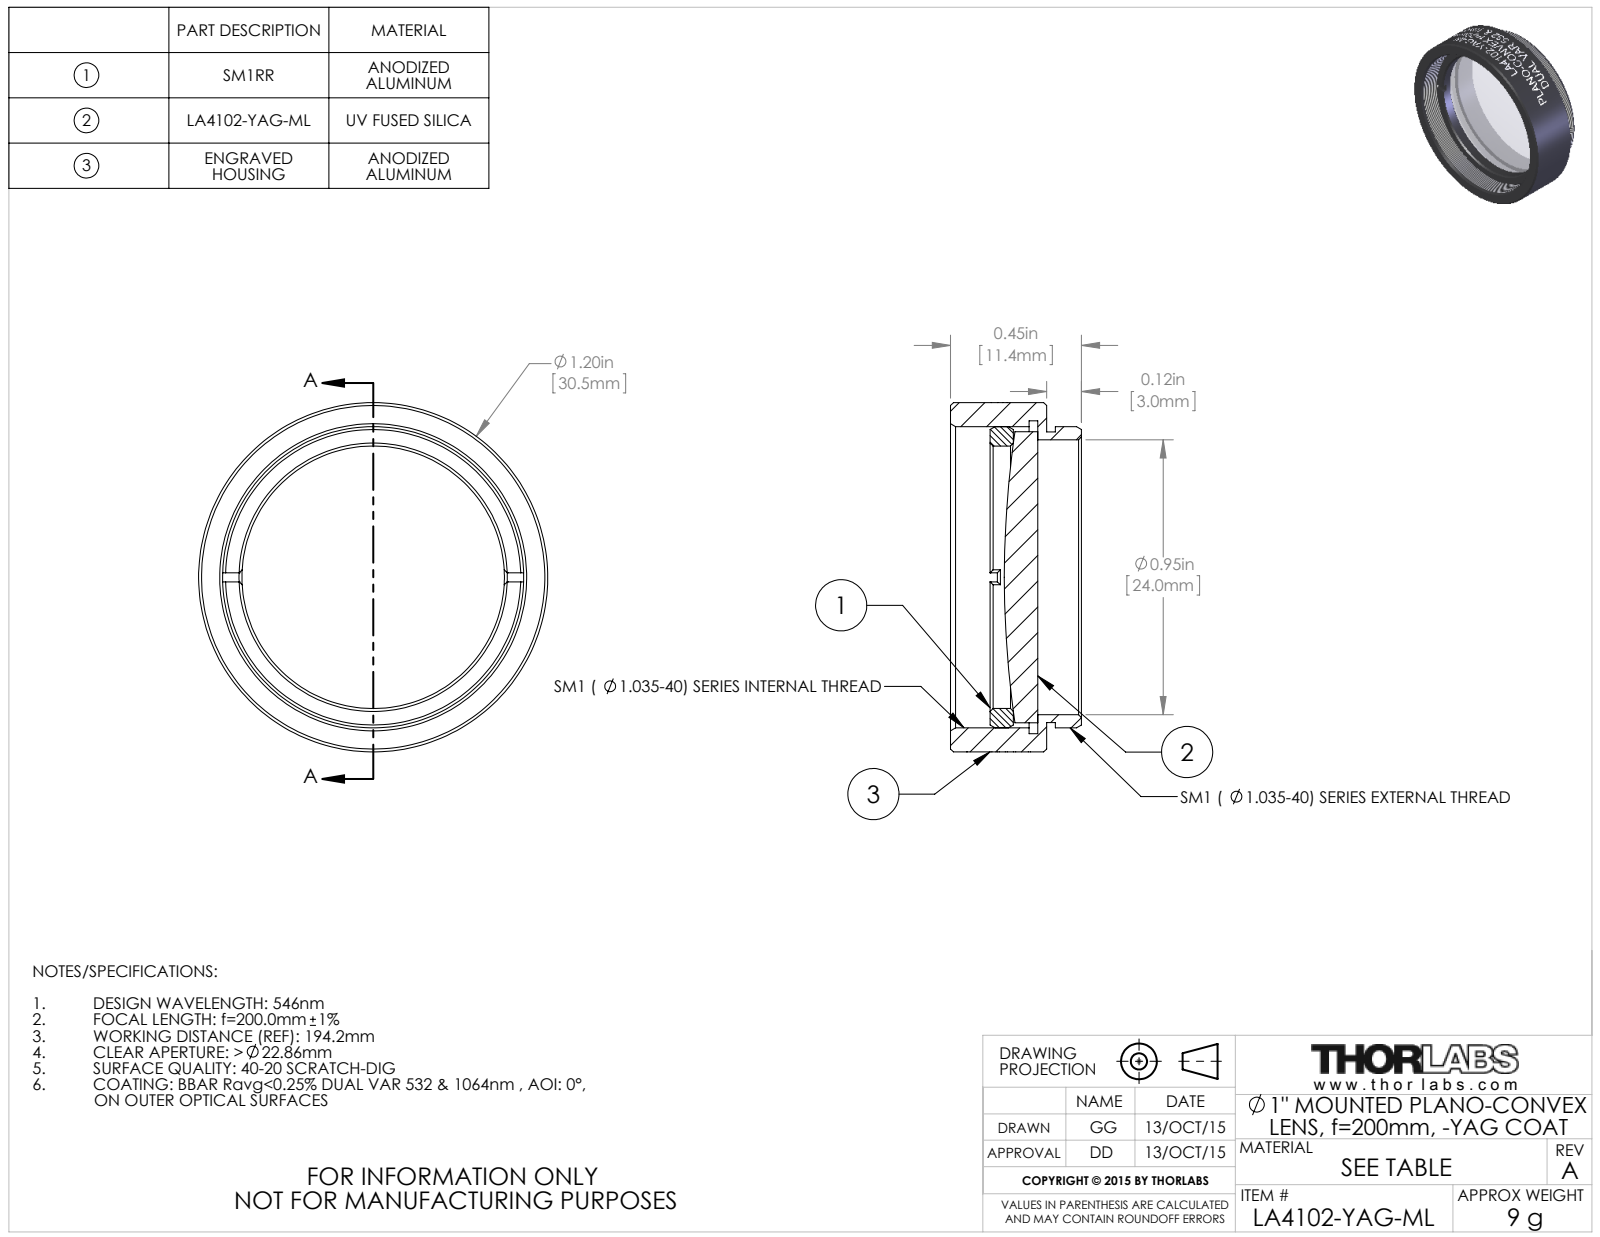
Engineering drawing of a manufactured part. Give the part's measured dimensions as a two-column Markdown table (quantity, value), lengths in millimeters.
| quantity | value |
| --- | --- |
| part name | TTN039156-E0W |
| STEP written by | SolidWorks 2014 (CONFIG_CONTROL_DESIGN) |
| units | millimeters |
| bodies | 3 solids, 154 faces (20 planar, 110 cylindrical, 24 other) |
| overall size | 30.48 × 30.48 × 11.43 |
| volume | 3 327 mm³ |
| surface area | 4 315 mm² |
| round holes (diameter × count) | 22.91 × 1, 24 × 1, 27.3 × 1 |
| round bosses / shafts (diameter × count) | 30.48 × 1, 26.29 × 1, 25.4 × 1, 25.37 × 1 |
| main face-to-face distances | 0.76, 8.38, 7.62, 2.9, 2.14, 5.48, 4.93, 4.17, 2.03, 3.45 |
